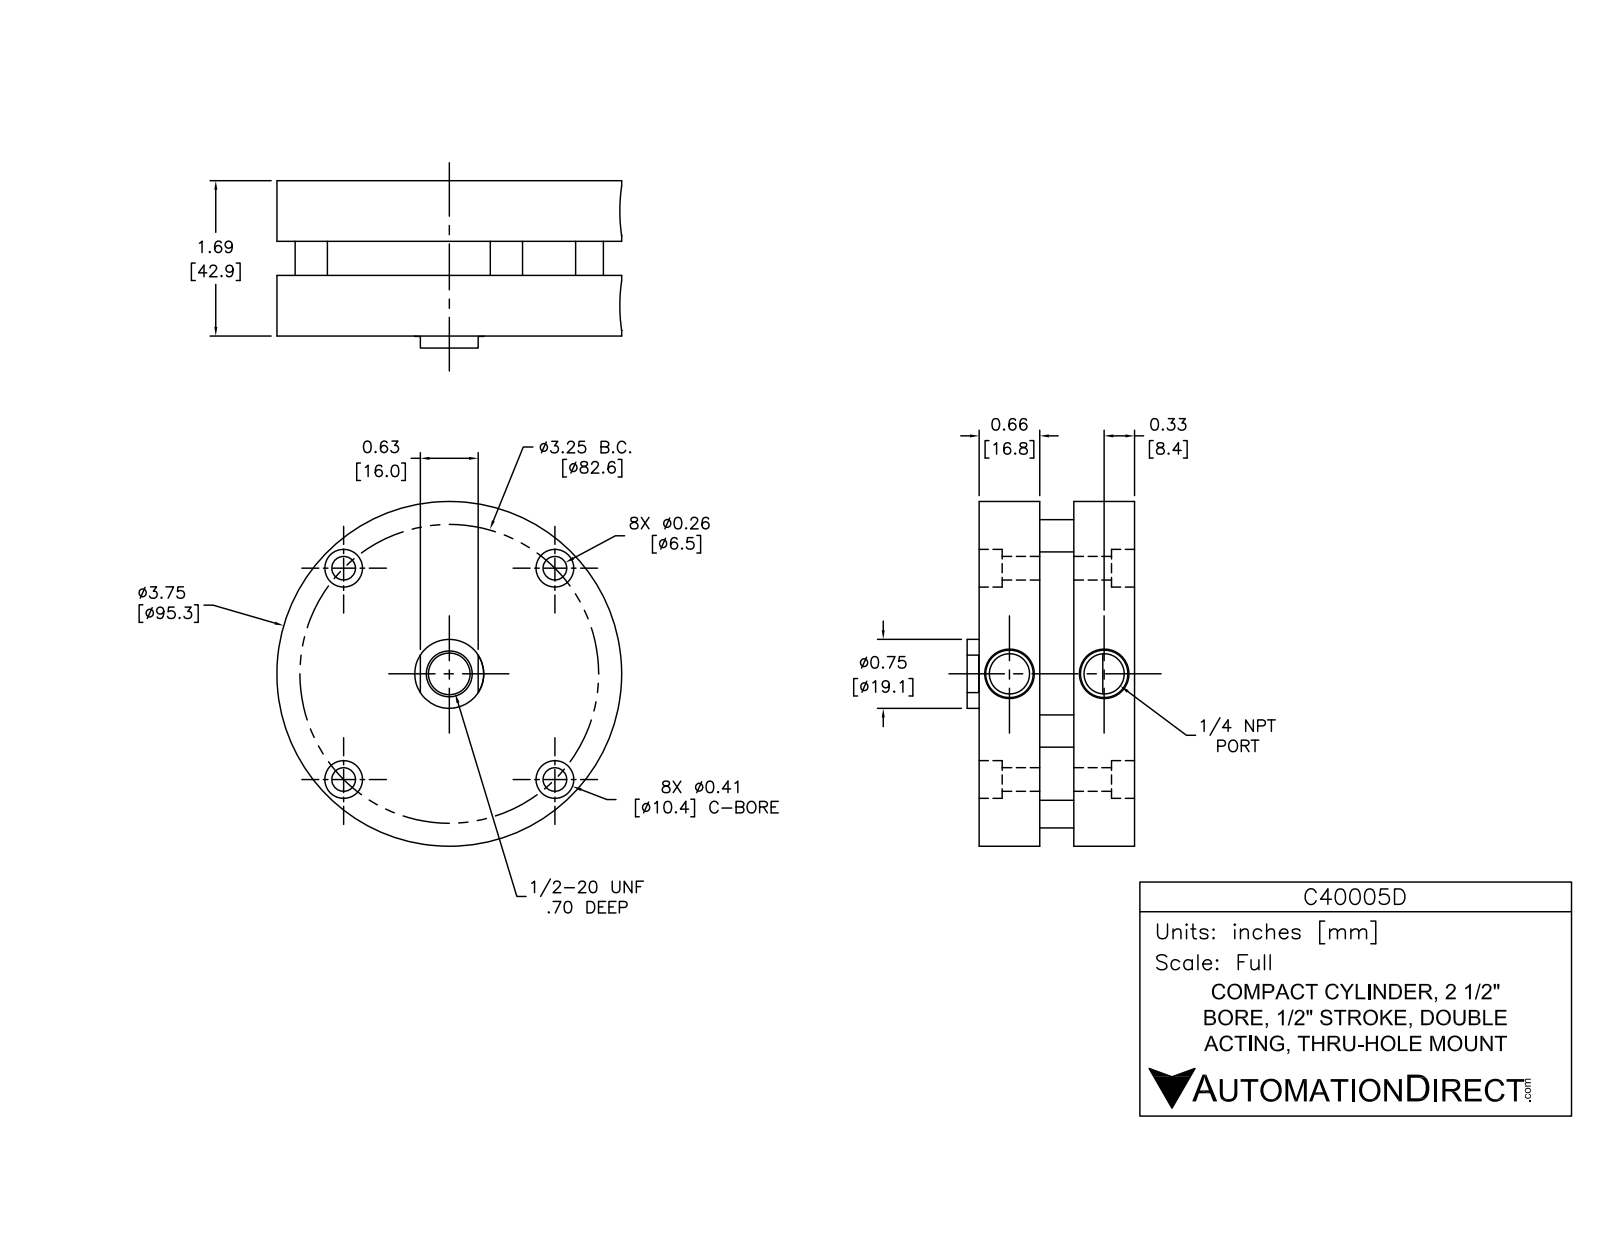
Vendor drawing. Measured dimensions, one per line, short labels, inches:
name: C40005D; C40005D-FO1_BM_rod; C40005D-FO1_BM_heads; C40005D-FO1_BM_tube (+3 more)
written by: SolidWorks 2014 (AUTOMOTIVE_DESIGN)
unit: in
bodies: 9 solids, 165 faces (49 planar, 98 cylindrical, 18 other)
size: 3.75 × 3.75 × 1.82
volume: 13.89 in³; area: 110.9 in²
holes: 4× ⌀0.225, 4× ⌀0.281, 4× ⌀0.406, 2× ⌀0.218, 1× ⌀0.446, 1× ⌀0.75, 1× ⌀0.752, 1× ⌀2.5, 1× ⌀2.639
bosses: 4× ⌀0.45, 4× ⌀0.225, 1× ⌀3.75
face distances: 0.387, 1.303, 1.69, 0.916, 1.03, 0.643, 0.273, 0.66, 0.66, 0.273
hole spacings: 0.48, 1.625, 1.625, 1.933, 2.298, 2.298, 2.613, 3.215
